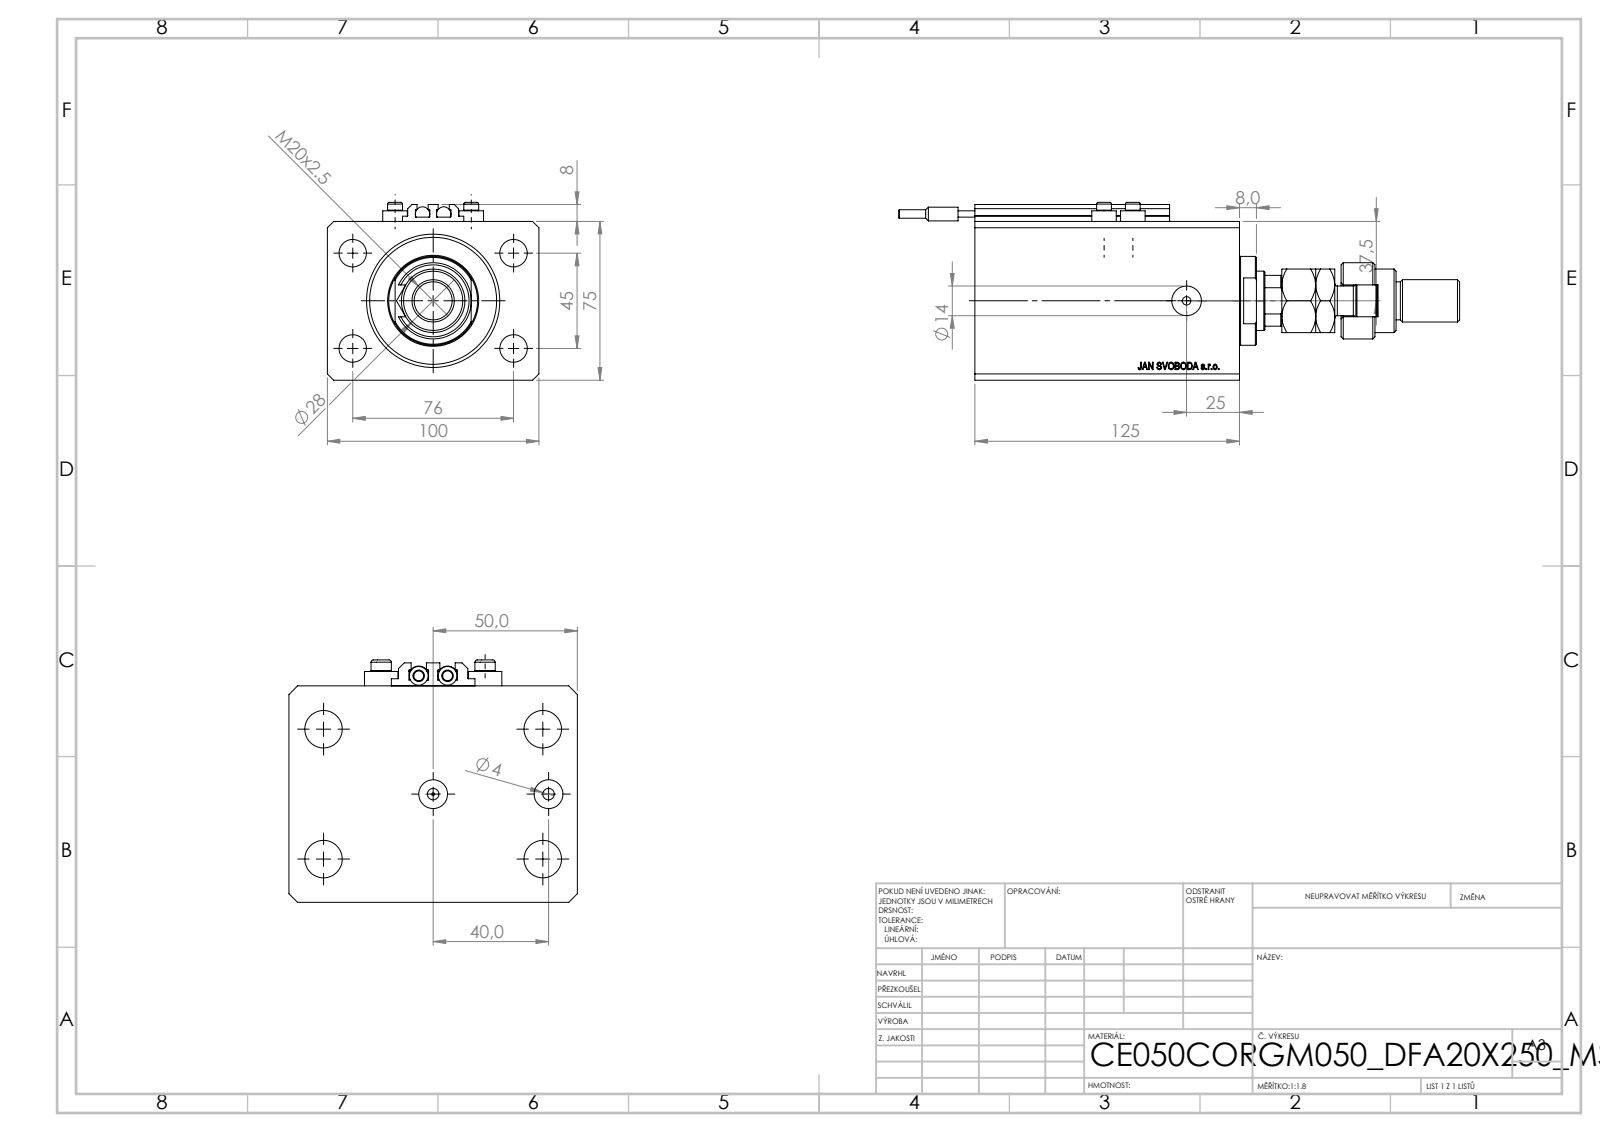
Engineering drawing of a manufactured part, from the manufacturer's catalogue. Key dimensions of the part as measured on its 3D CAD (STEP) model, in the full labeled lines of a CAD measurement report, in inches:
Part name (STEP PRODUCT): V250CE_C_VCP; V250CE_VC_C; V250CE_C_Body; FEMALE_PART_FOR_DFA (+3 more)
STEP written by: SolidWorks 2019 (CONFIG_CONTROL_DESIGN)
Units: inches
Bodies: 12 solids, 1175 faces (564 planar, 113 cylindrical, 498 other)
Overall size (bounding box): 10.429 × 3.937 × 3.307
Volume: 53.21 in³ · Surface area: 249 in²
Round holes (diameter × count): ⌀0.157 ×8, ⌀0.512 ×4, ⌀0.394 ×2, ⌀0.551 ×2, ⌀0.049 ×1, ⌀0.728 ×1, ⌀1.102 ×1, ⌀1.969 ×1, ⌀2.48 ×1
Round bosses / shafts (diameter × count): ⌀0.457 ×4, ⌀0.276 ×4, ⌀0.268 ×2, ⌀0.256 ×2, ⌀0.157 ×2, ⌀1.654 ×1, ⌀1.417 ×1, ⌀1.181 ×1
Partial cylindrical surfaces — rounded edges, fillets, slot ends (radius × count): R0.008 ×10, R0.295 ×1, R0.472 ×1, R0.531 ×1
Main face-to-face distances: 2.953, 3.937, 4.921, 0.469, 4.453, 3.874, 3.406, 1.047, 0.118, 0.394
Hole centre spacings: 1.739, 0.535, 0.889, 1.417, 1.515, 1.772, 2.992, 3.196
